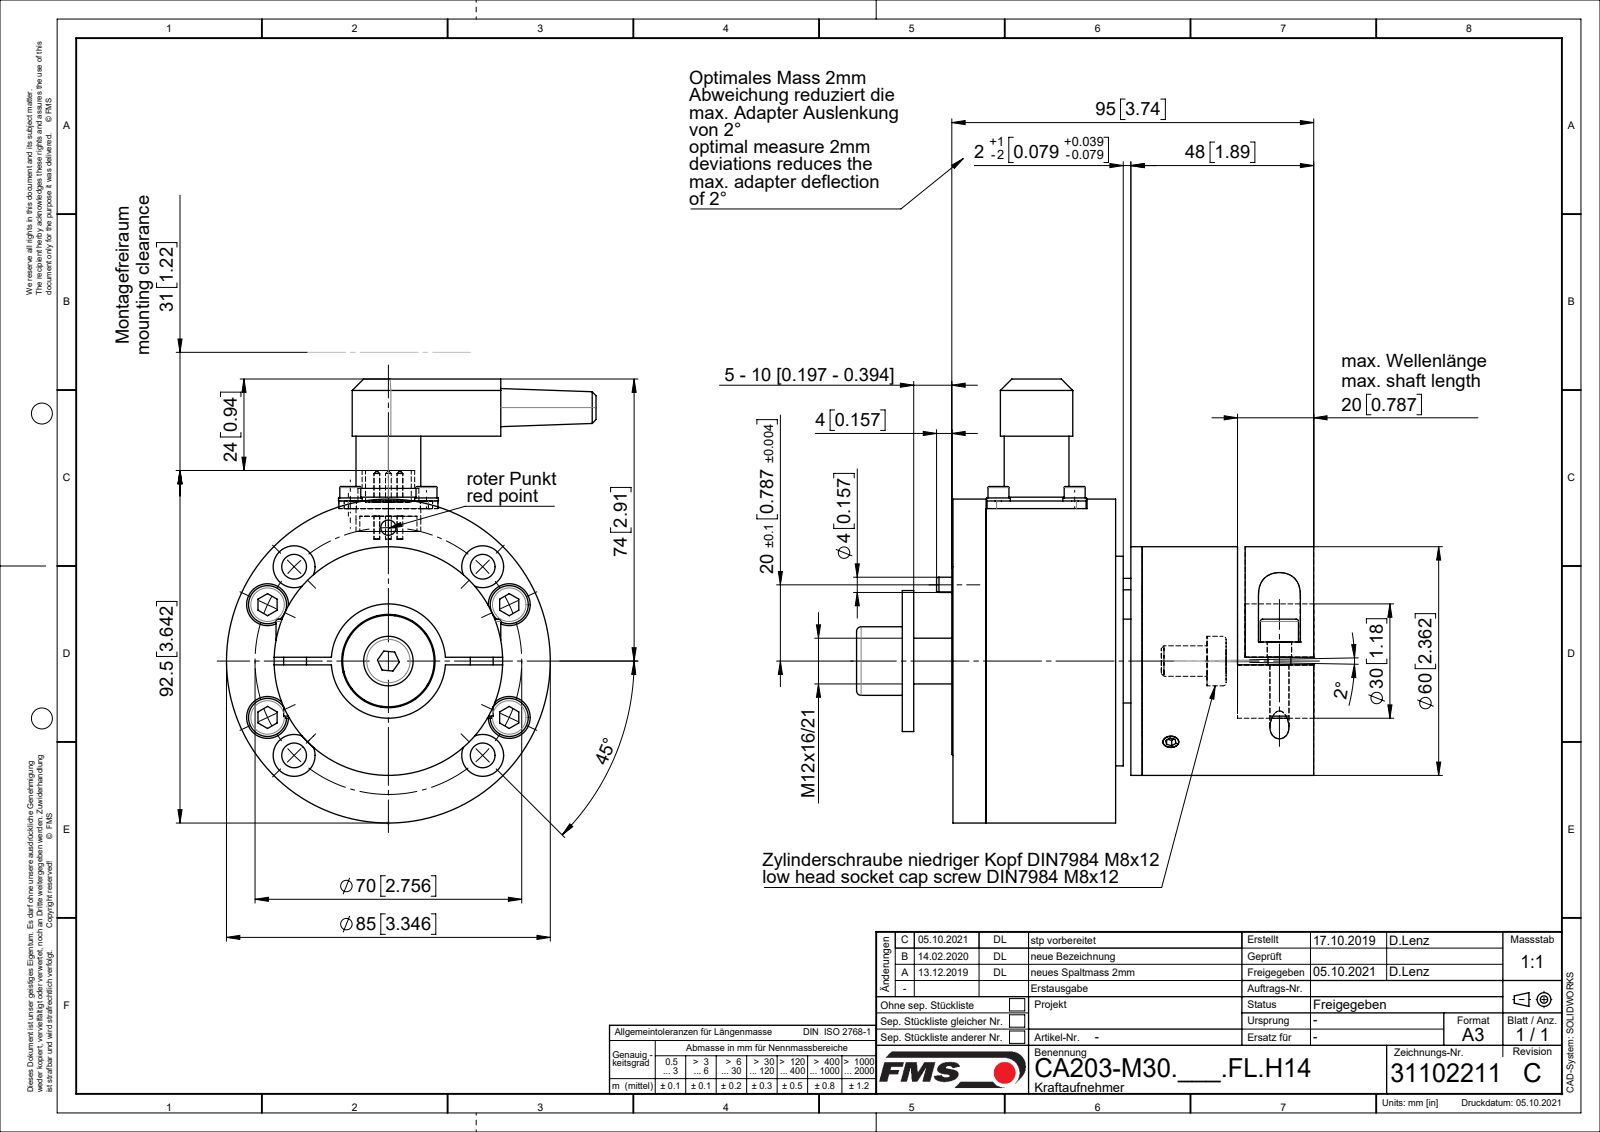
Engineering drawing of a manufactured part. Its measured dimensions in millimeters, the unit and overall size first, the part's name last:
Units: millimetres
Overall size (bounding box): 120 × 116.5 × 97
Round holes (diameter × count): ⌀2.5 ×8, ⌀6.5 ×8, ⌀11 ×8, ⌀5 ×6, ⌀2 ×5, ⌀4 ×5, ⌀3.1 ×4, ⌀3.2 ×4, ⌀3.6 ×4, ⌀7 ×4, ⌀3 ×2, ⌀6.4 ×2
Round bosses / shafts (diameter × count): ⌀3 ×8, ⌀6 ×7, ⌀10 ×6, ⌀1.5 ×5, ⌀6.2 ×4, ⌀5.7 ×4, ⌀5.5 ×4, ⌀85 ×1
Partial cylindrical surfaces — rounded edges, fillets, slot ends (radius × count): R2.5 ×4, R5 ×2, R5.5 ×2, R9.5 ×1
Main face-to-face distances: 2, 41, 45, 10, 30, 3, 60, 34, 50, 22
Hole centre spacings: 35, 20, 24.78, 25.2, 32.8, 51.14, 56.46, 6
Volume: 311 358 mm³ · Surface area: 113 718 mm²
Bodies: 43 solids, 803 faces (278 planar, 333 cylindrical, 192 other)
Part name (STEP PRODUCT): RKL_6203_01; 061205-3_01; 091113-3_stp_01; Zyl-Schr DIN7984_M8x12 (+8 more)
STEP written by: SolidWorks 2018 (CONFIG_CONTROL_DESIGN)
